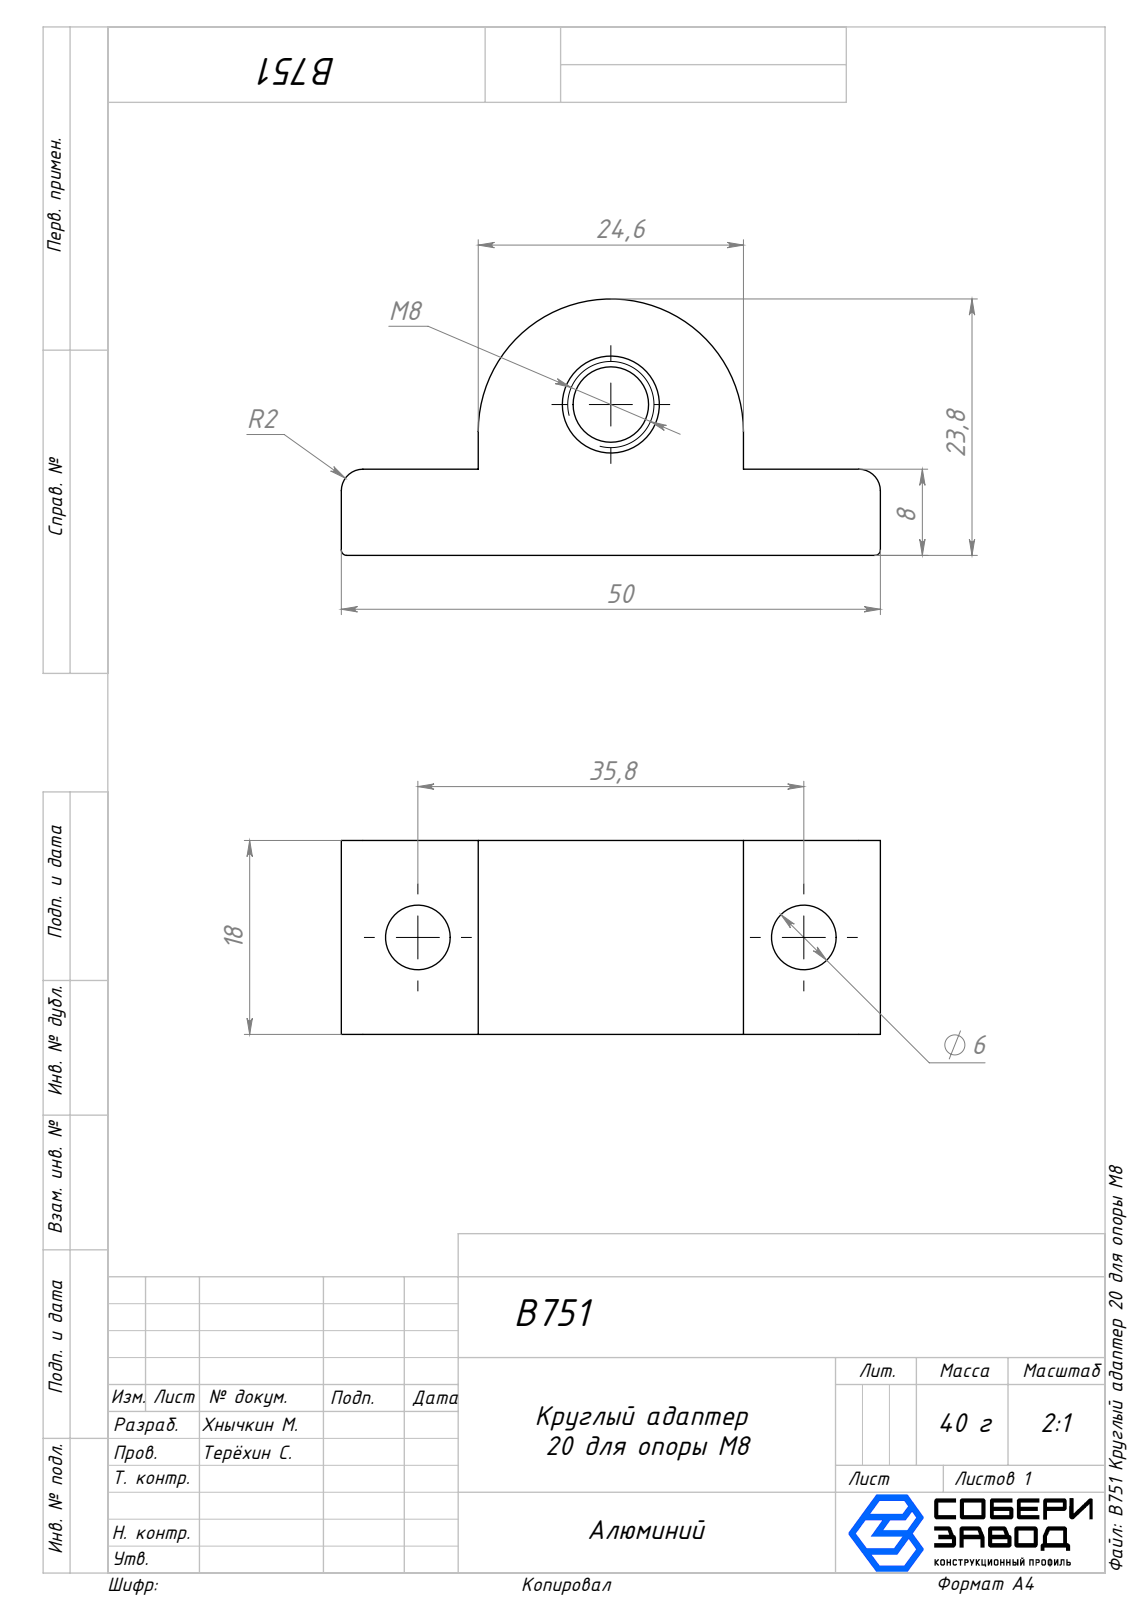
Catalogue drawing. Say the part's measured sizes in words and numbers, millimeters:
The part is named "B751 Круглый адаптер 20 для опоры М8". Its 3-D file was written by "SolidWorks 2025 (AUTOMOTIVE_DESIGN)". It is 1 solid with 24 faces: 9 planar, 11 cylindrical and 4 other. Overall it measures 50 by 23.8 by 18 millimeters. Its volume is 11 825 cubic millimeters and its surface area 4 356 square millimeters. Round holes: 2 of diameter 6, 1 of diameter 7. Partial cylindrical surfaces (rounded edges, fillets, slot ends): 2 of radius 0.5, 2 of radius 2, 1 of radius 12.3. The main face-to-face distances are 18, 8, 12.7, 37.3, 50, 24.6. The hole center spacings are 35.8.
